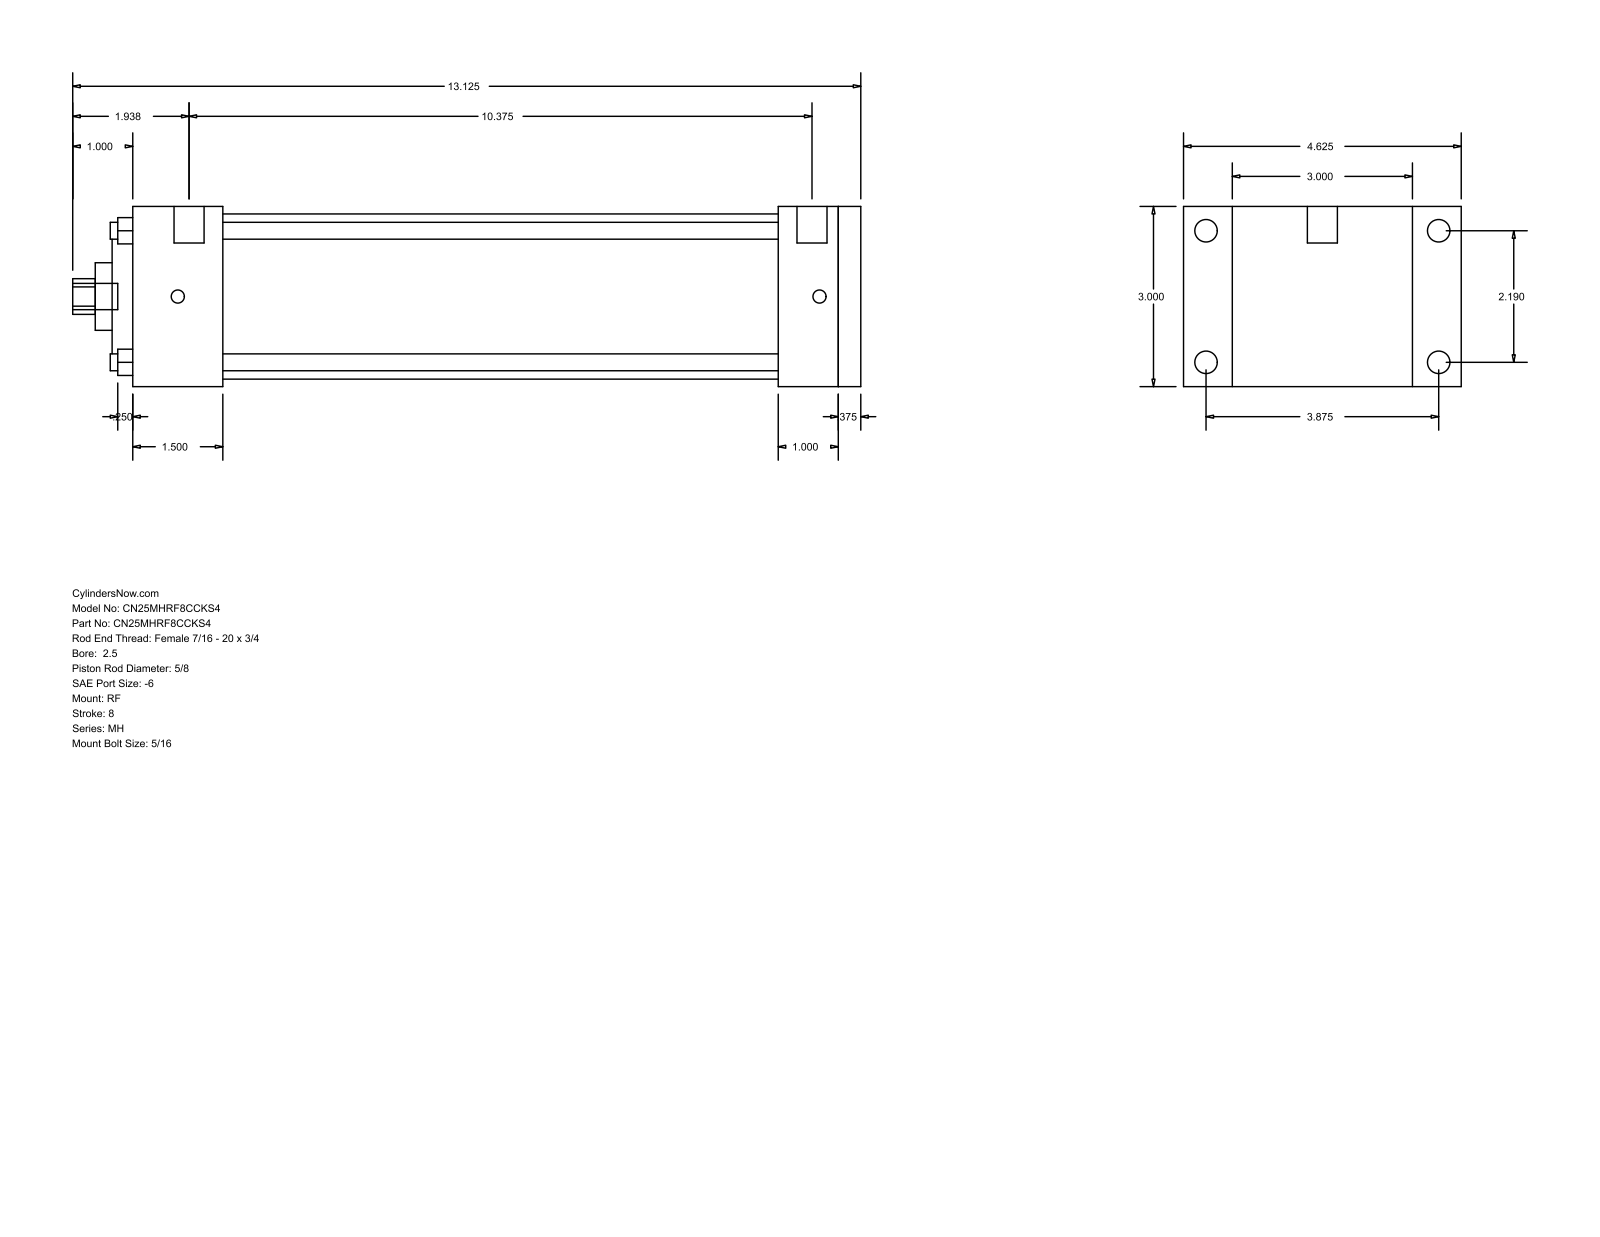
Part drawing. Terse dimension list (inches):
name: MH_RF__0250_0.625
written by: GSSL Pune (CONFIG_CONTROL_DESIGN)
unit: in
bodies: 0 solids, 94 faces (65 planar, 29 cylindrical, 0 other)
size: 13.125 × 4.625 × 3
holes: 4× ⌀0.281, 1× ⌀0.625, 1× ⌀1.125, 1× ⌀2.187, 1× ⌀2.75
bosses: 4× ⌀0.375, 4× ⌀0.219, 2× ⌀0.5, 1× ⌀0.437
rounds: 1× R0.297
face distances: 3, 0.375, 12.125, 11.75, 1, 10.75, 1.375, 1.5, 9.25, 10.25
hole spacings: 1.548, 2.19, 3.097
